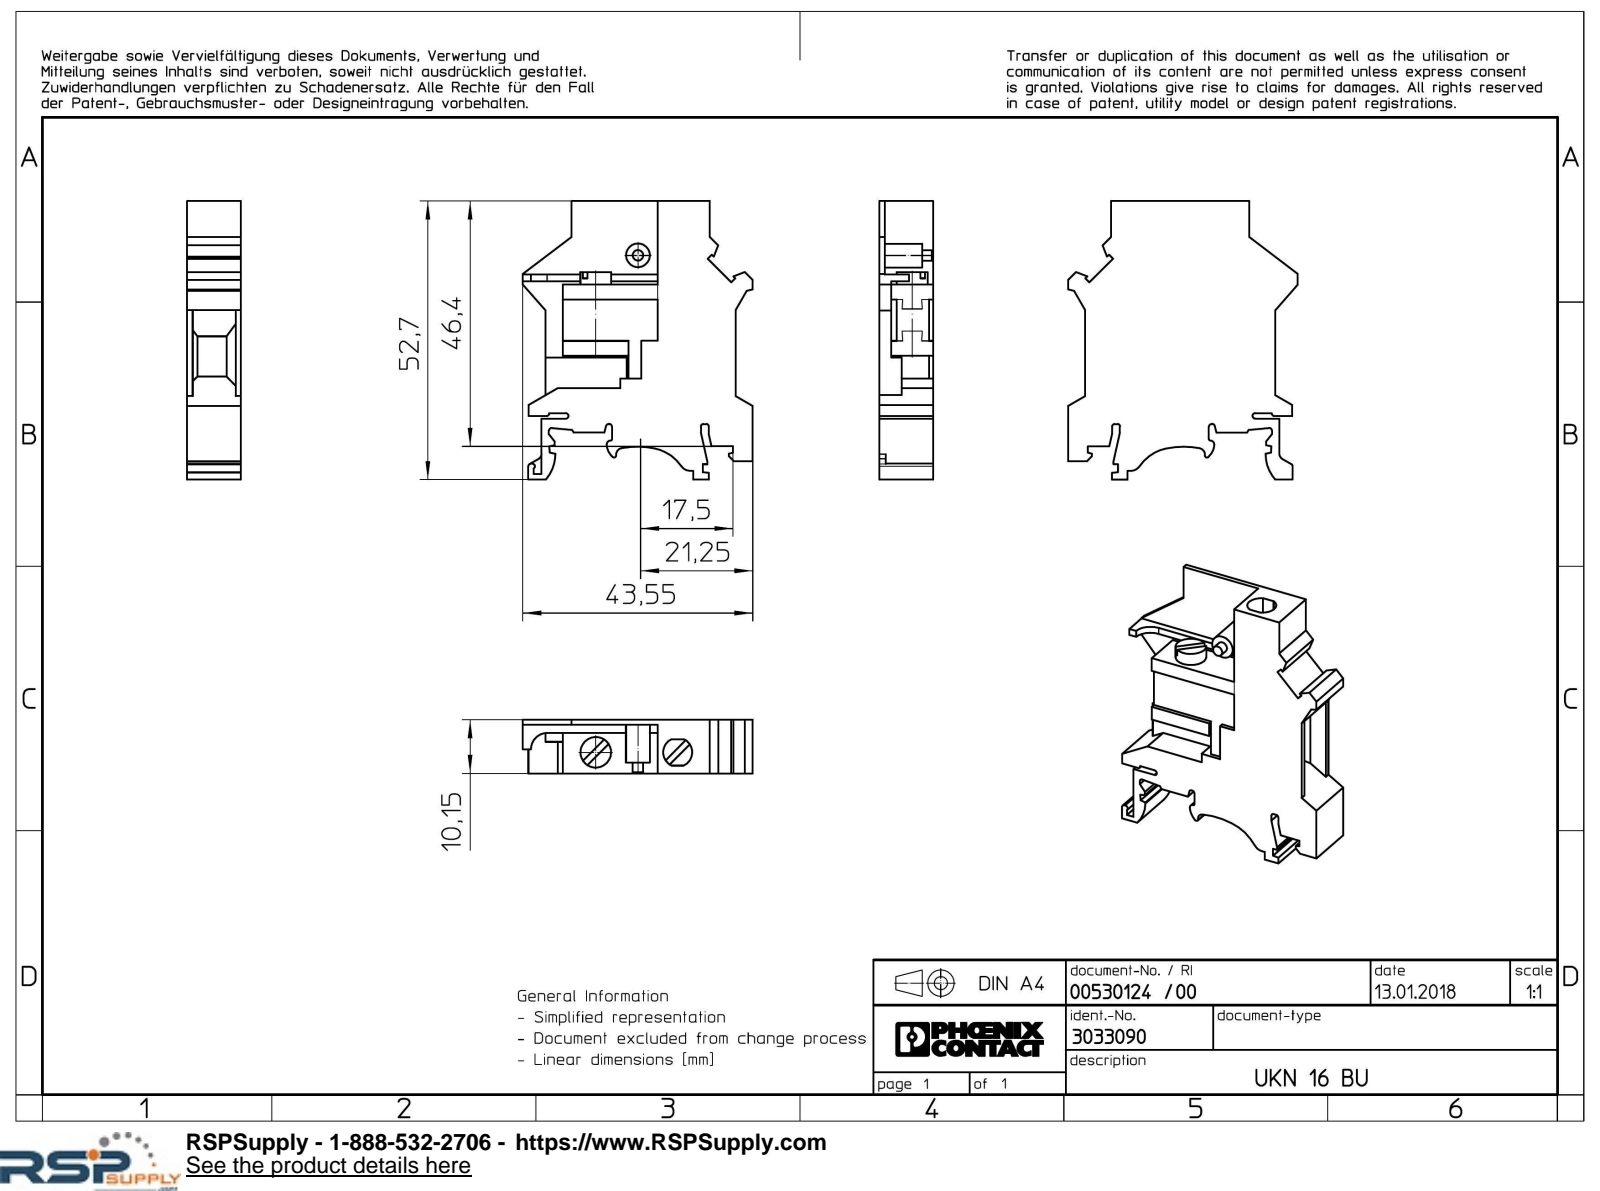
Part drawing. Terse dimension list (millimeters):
name: UKN_16_BU-select
written by: Creo Elements/Direct Modeling 18.1I 14-Aug-2016 (C) Parametric Technology GmbH (AUTOMOTIVE_DESIGN)
unit: mm
bodies: 1 solid, 156 faces (127 planar, 29 cylindrical, 0 other)
size: 52.7 × 43.55 × 10.15
volume: 11 841 mm³; area: 7 273 mm²
bosses: 1× ⌀5.8, 1× ⌀4.5, 1× ⌀2
rounds: 8× R0.5, 1× R0.3, 1× R0.4, 1× R0.52, 1× R0.53, 1× R0.7, 1× R1, 1× R1.2
face distances: 10.15, 1, 2.25, 3.25, 9.15, 18, 1.25, 7.1, 7.9, 0.8
